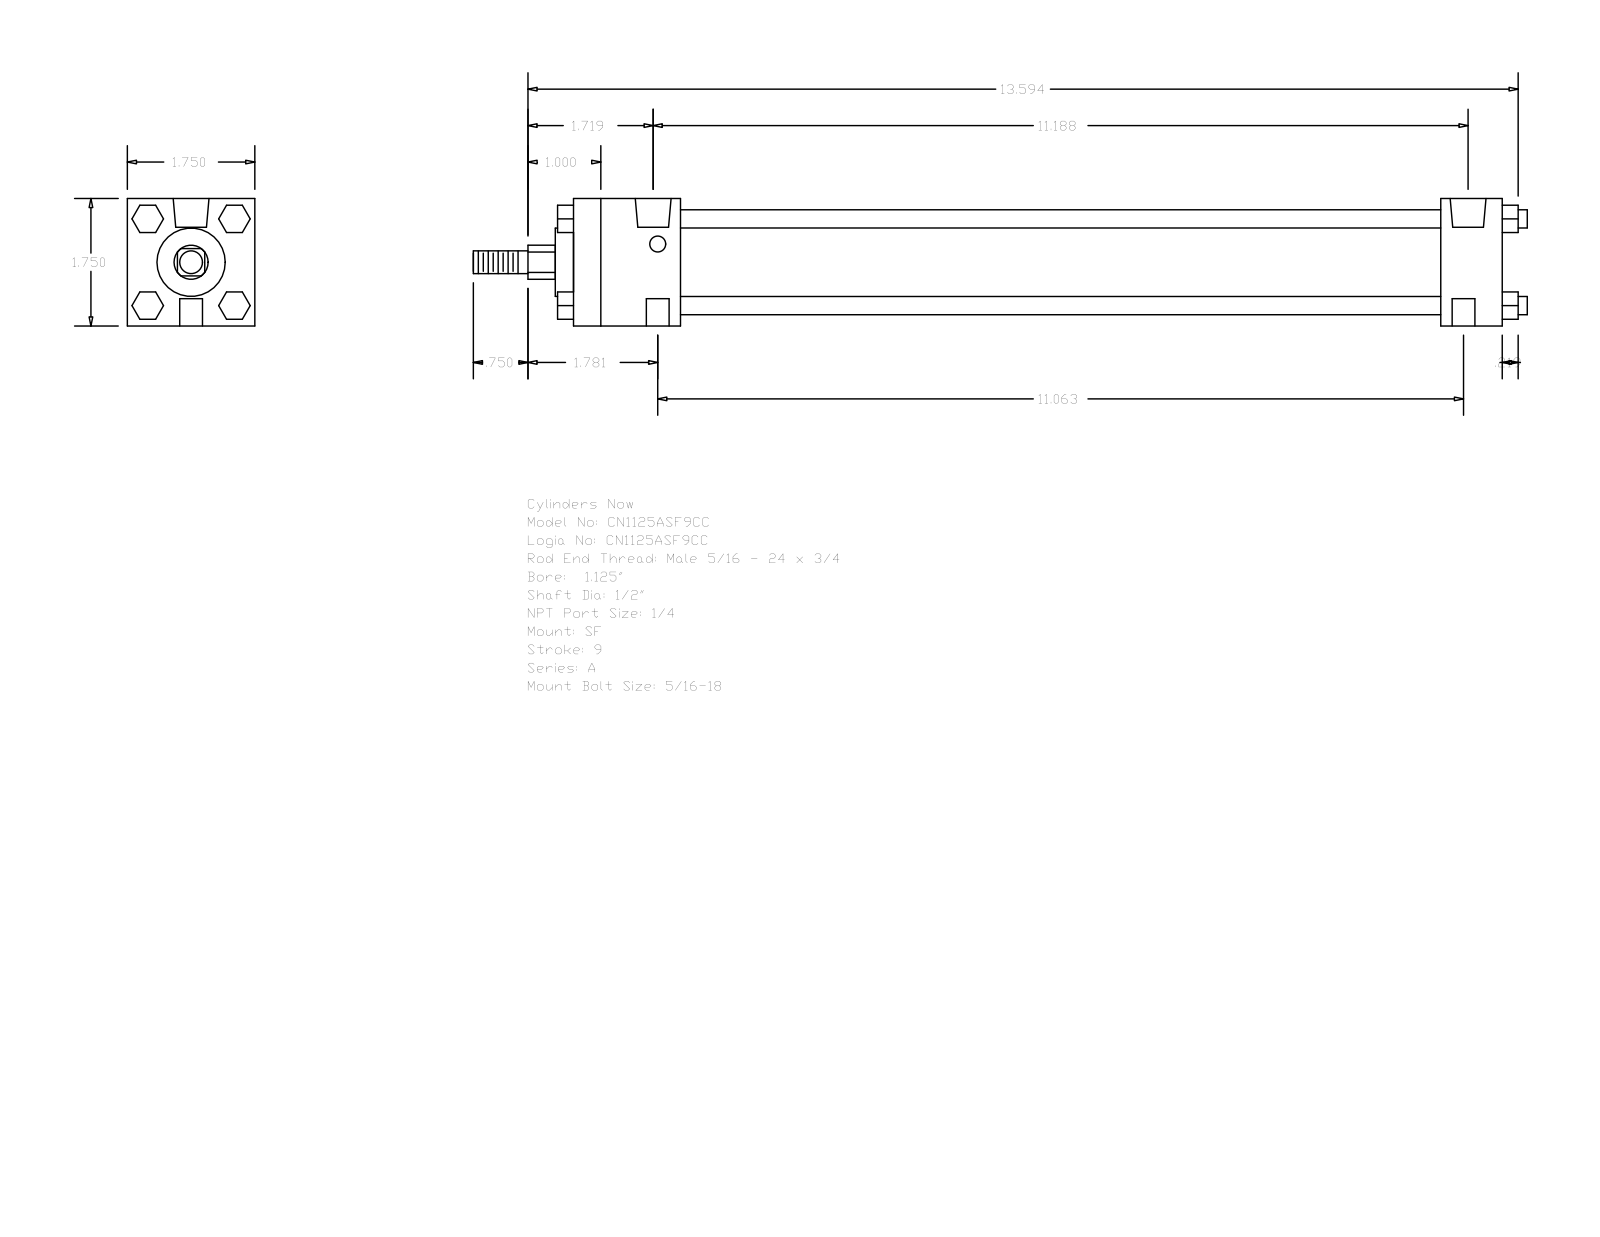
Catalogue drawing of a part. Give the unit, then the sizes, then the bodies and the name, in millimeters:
Units: millimetres
Overall size (bounding box): 367.51 × 44.45 × 44.45
Round holes (diameter × count): ⌀5.56 ×2, ⌀7.94 ×2, ⌀12.49 ×2
Round bosses / shafts (diameter × count): ⌀6.35 ×4, ⌀31.88 ×1, ⌀23.81 ×1, ⌀12.7 ×1, ⌀7.94 ×1
Partial cylindrical surfaces — rounded edges, fillets, slot ends (radius × count): R5.94 ×1
Main face-to-face distances: 44.46, 323.85, 302.41, 21.44, 37.3, 265.11, 286.55, 9.53, 5.59, 26.99
Hole centre spacings: 280.99, 1.58, 1.59, 282.57, 282.58, 284.16
Bodies: 0 solids, 120 faces (92 planar, 28 cylindrical, 0 other)
Part name (STEP PRODUCT): A_SF__0112_0.5
STEP written by: GSSL Pune (CONFIG_CONTROL_DESIGN)
